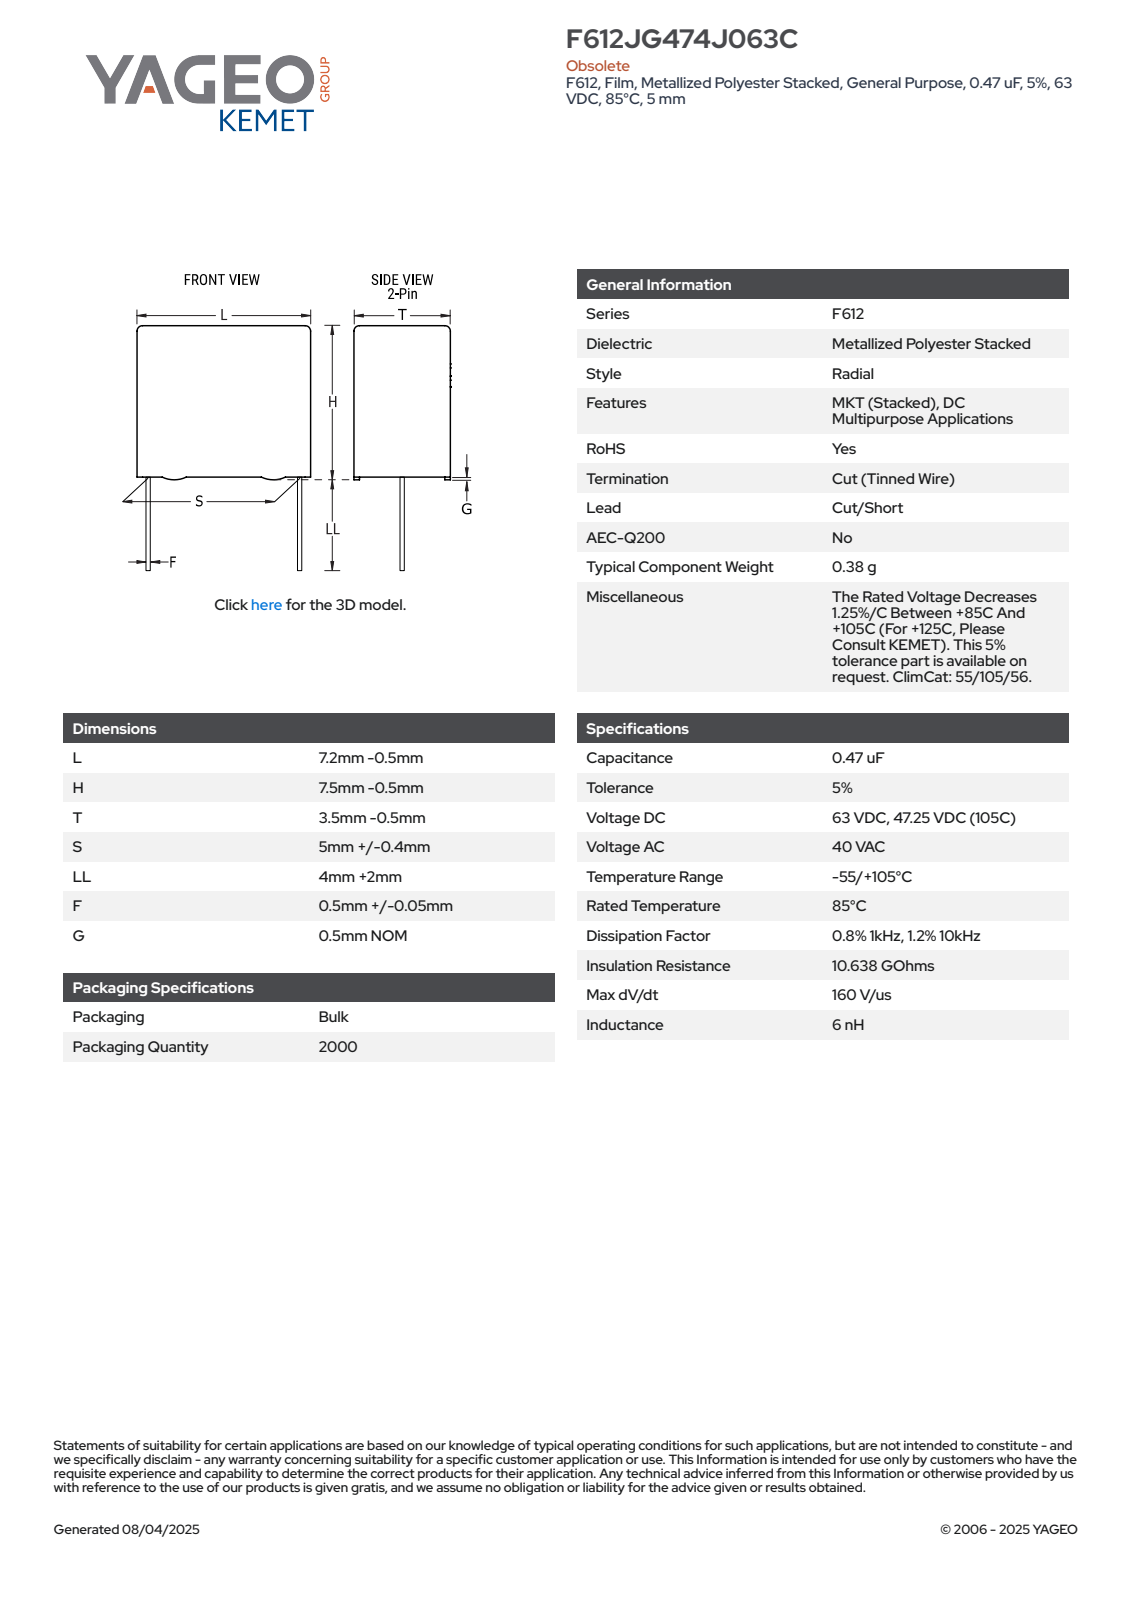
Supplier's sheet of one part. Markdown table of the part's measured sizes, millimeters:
| quantity | value |
| --- | --- |
| part name | CFR_RBG_7.2X7.5X3.5_L6.7H7T3S5LL6F0.55G0.5 |
| STEP written by | SolidWorks 2021 (AUTOMOTIVE_DESIGN) |
| units | millimeters |
| bodies | 4 solids, 89 faces (81 planar, 8 cylindrical, 0 other) |
| overall size | 13 × 6.7 × 3 |
| volume | 133 mm³ |
| surface area | 195 mm² |
| round bosses / shafts (diameter × count) | 0.55 × 2 |
| partial cylindrical surfaces (radius × count) | 0.5 × 4 |
| main face-to-face distances | 3, 6.7, 6.5, 2.83, 2.66, 0.5, 7, 6, 13, 2.49 |
